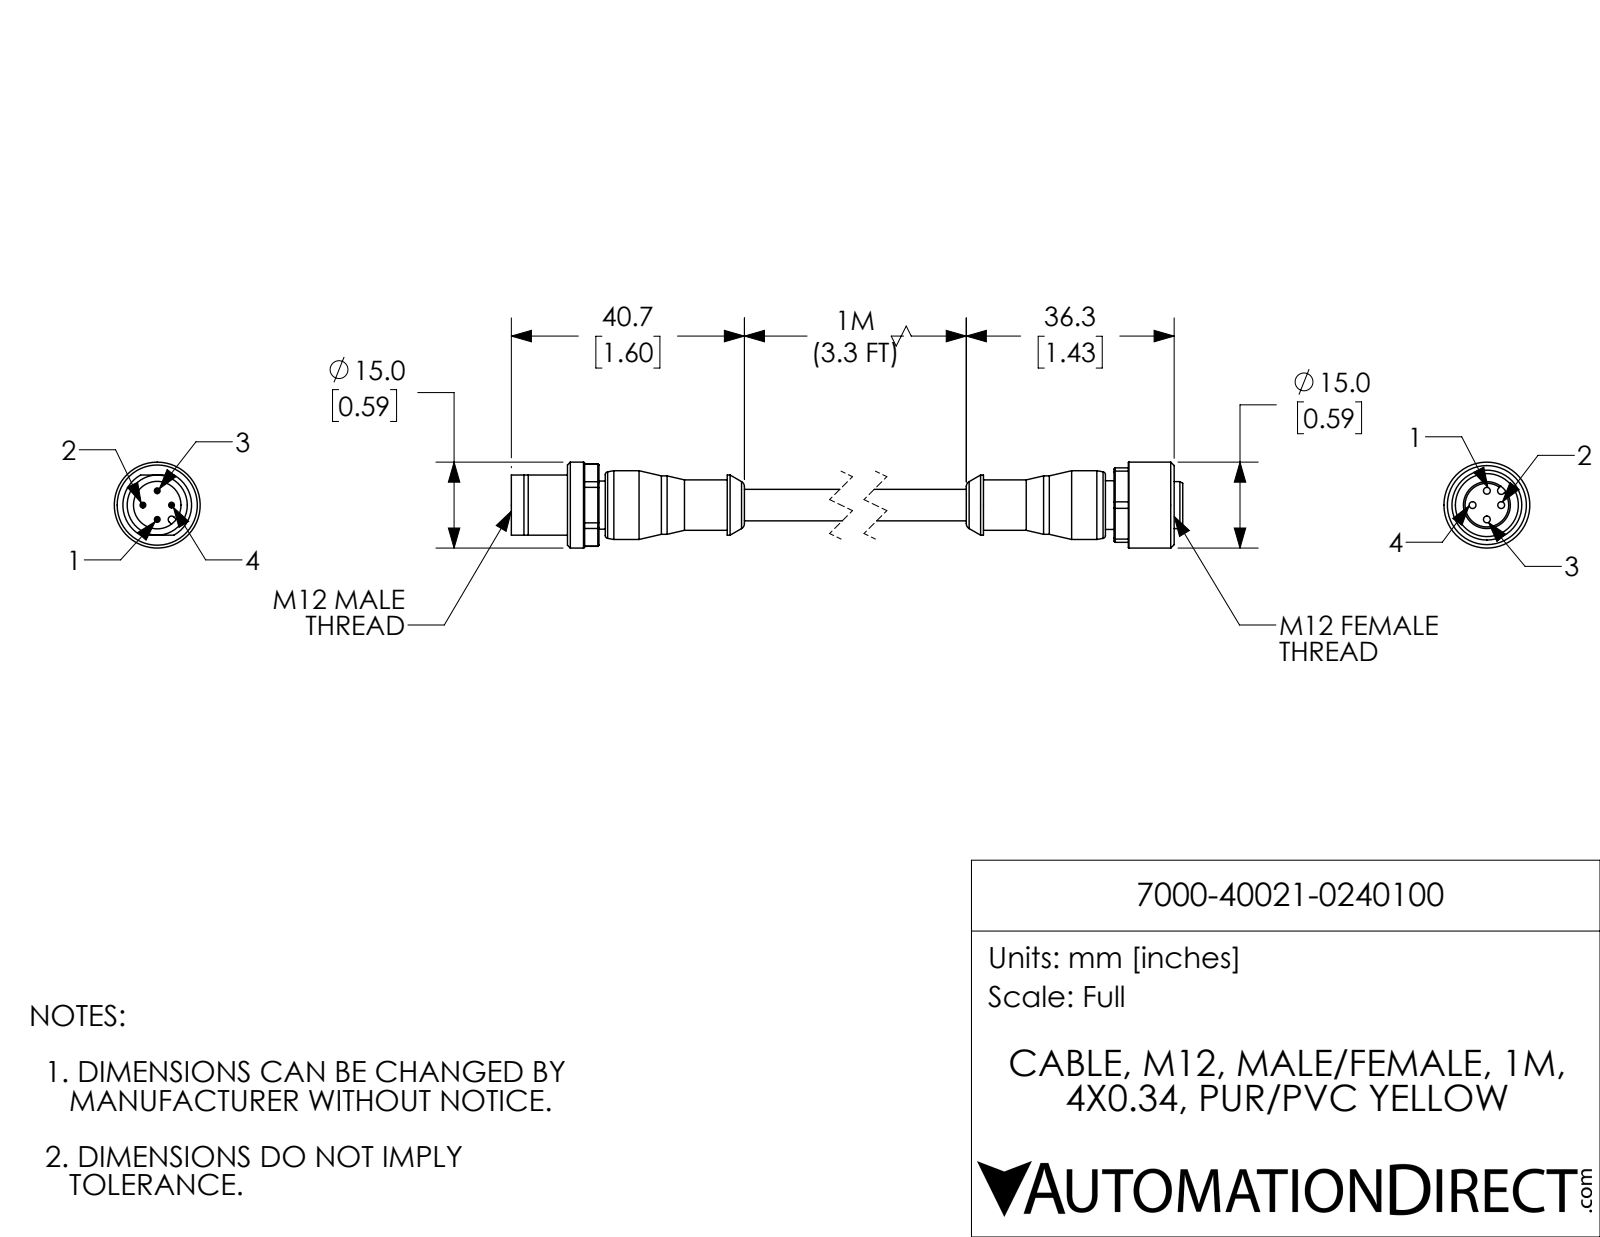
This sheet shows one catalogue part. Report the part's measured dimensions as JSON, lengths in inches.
{"part_name": "7000-40021-0240100_FEMALE; 7000-40021-0240100_MALE; 7000-40021-0240100", "step_written_by": "SolidWorks 2017 (AUTOMOTIVE_DESIGN)", "units": "inches", "bodies": {"solids": 2, "faces": 188, "planar": 58, "cylindrical": 69, "other": 61}, "overall_size": [5.138, 0.591, 0.591], "volume_in3": 0.488, "surface_area_in2": 7.93, "round_holes": [[0.047, 4], [0.327, 1], [0.433, 1]], "round_bosses_or_shafts": [[0.039, 4], [0.591, 1], [0.472, 1], [0.413, 1], [0.402, 1], [0.346, 1], [0.335, 1], [0.331, 1]], "partial_cylinders_radius": [[0.024, 1], [0.026, 1], [0.283, 1]], "face_to_face_distances": [0.472, 0.512, 0.118, 4.063, 0.413, 4.433, 2.217, 4.28, 0.295, 0.059], "hole_center_spacings": [0.098, 0.139, 0.197]}
